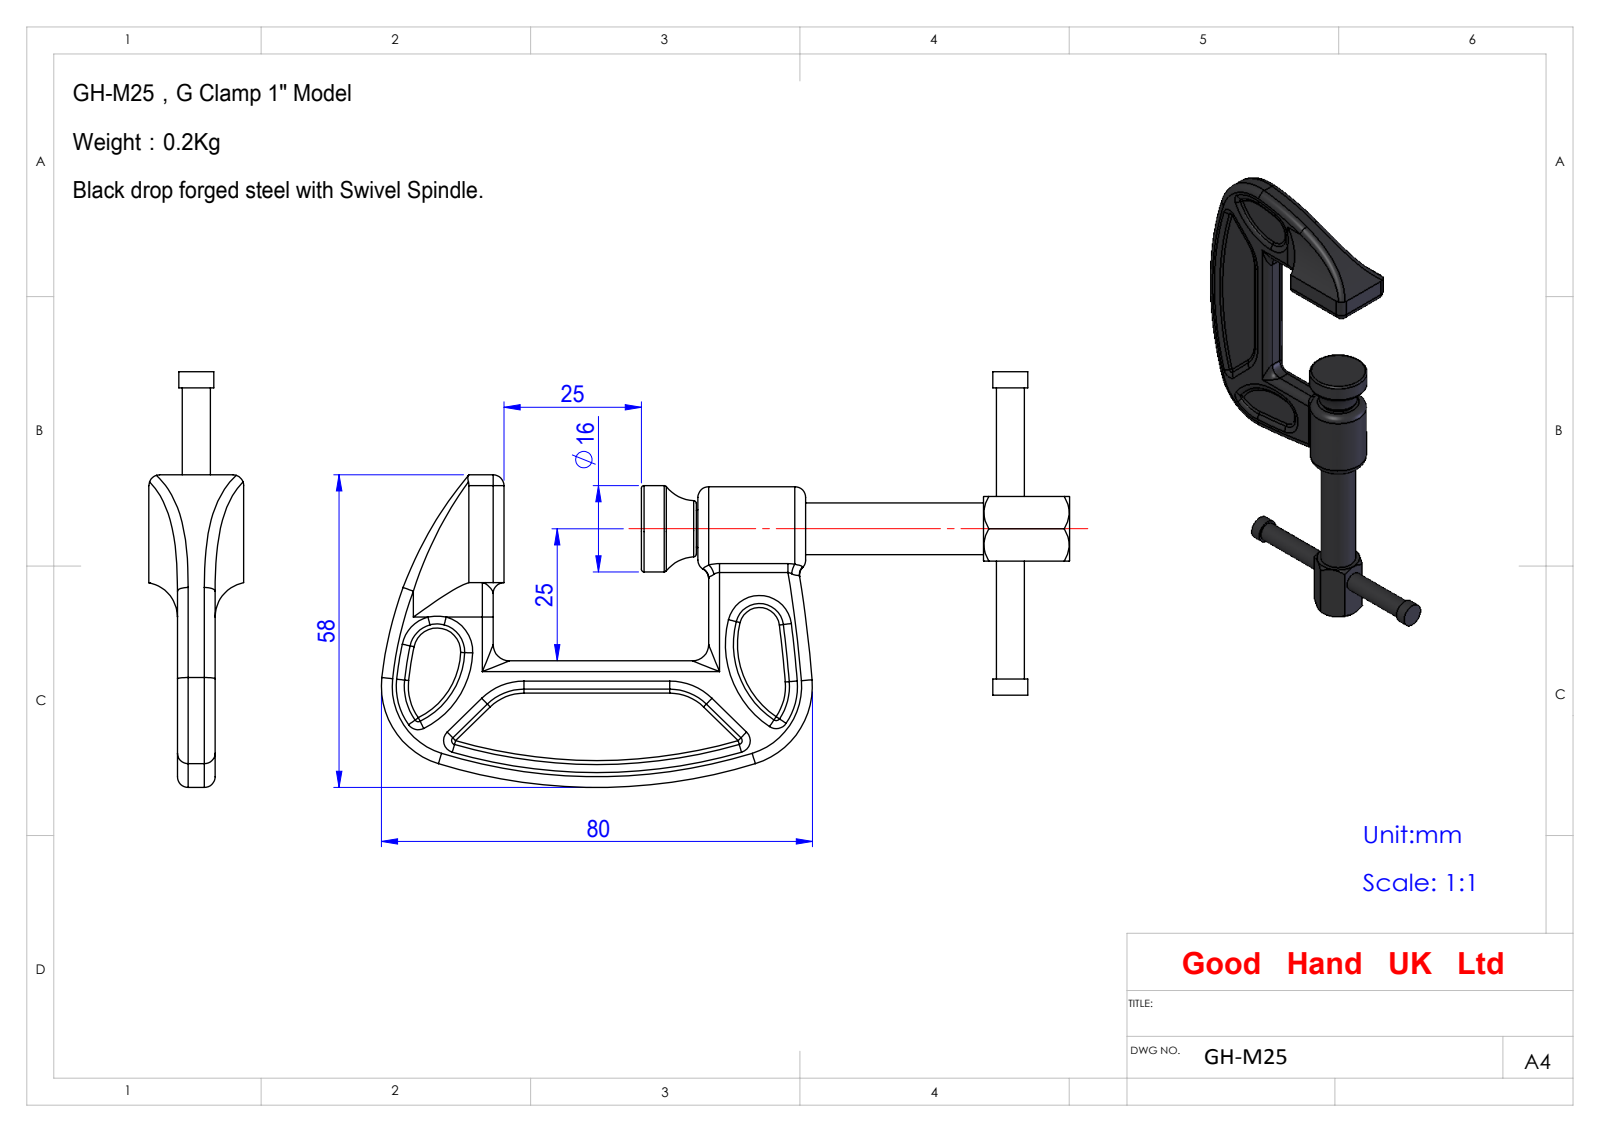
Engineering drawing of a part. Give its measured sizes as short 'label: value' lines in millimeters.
name: GH-M25
written by: SolidWorks 2008 (CONFIG_CONTROL_DESIGN)
unit: mm
bodies: 3 solids, 201 faces (29 planar, 57 cylindrical, 115 other)
size: 125.2 × 73.72 × 17.6
volume: 8 395 mm³; area: 12 316 mm²
holes: 1× ⌀5.2, 1× ⌀7, 1× ⌀9.6
bosses: 1× ⌀16, 1× ⌀15.6, 1× ⌀6.5, 1× ⌀5.2
rounds: 23× R2, 3× R1, 2× R3, 2× R6.5, 2× R12.72, 2× R15, 1× R70, 1× R100
face distances: 6, 7, 1, 25.5, 12, 5.3, 12.3, 105.2, 79.7, 12.01
